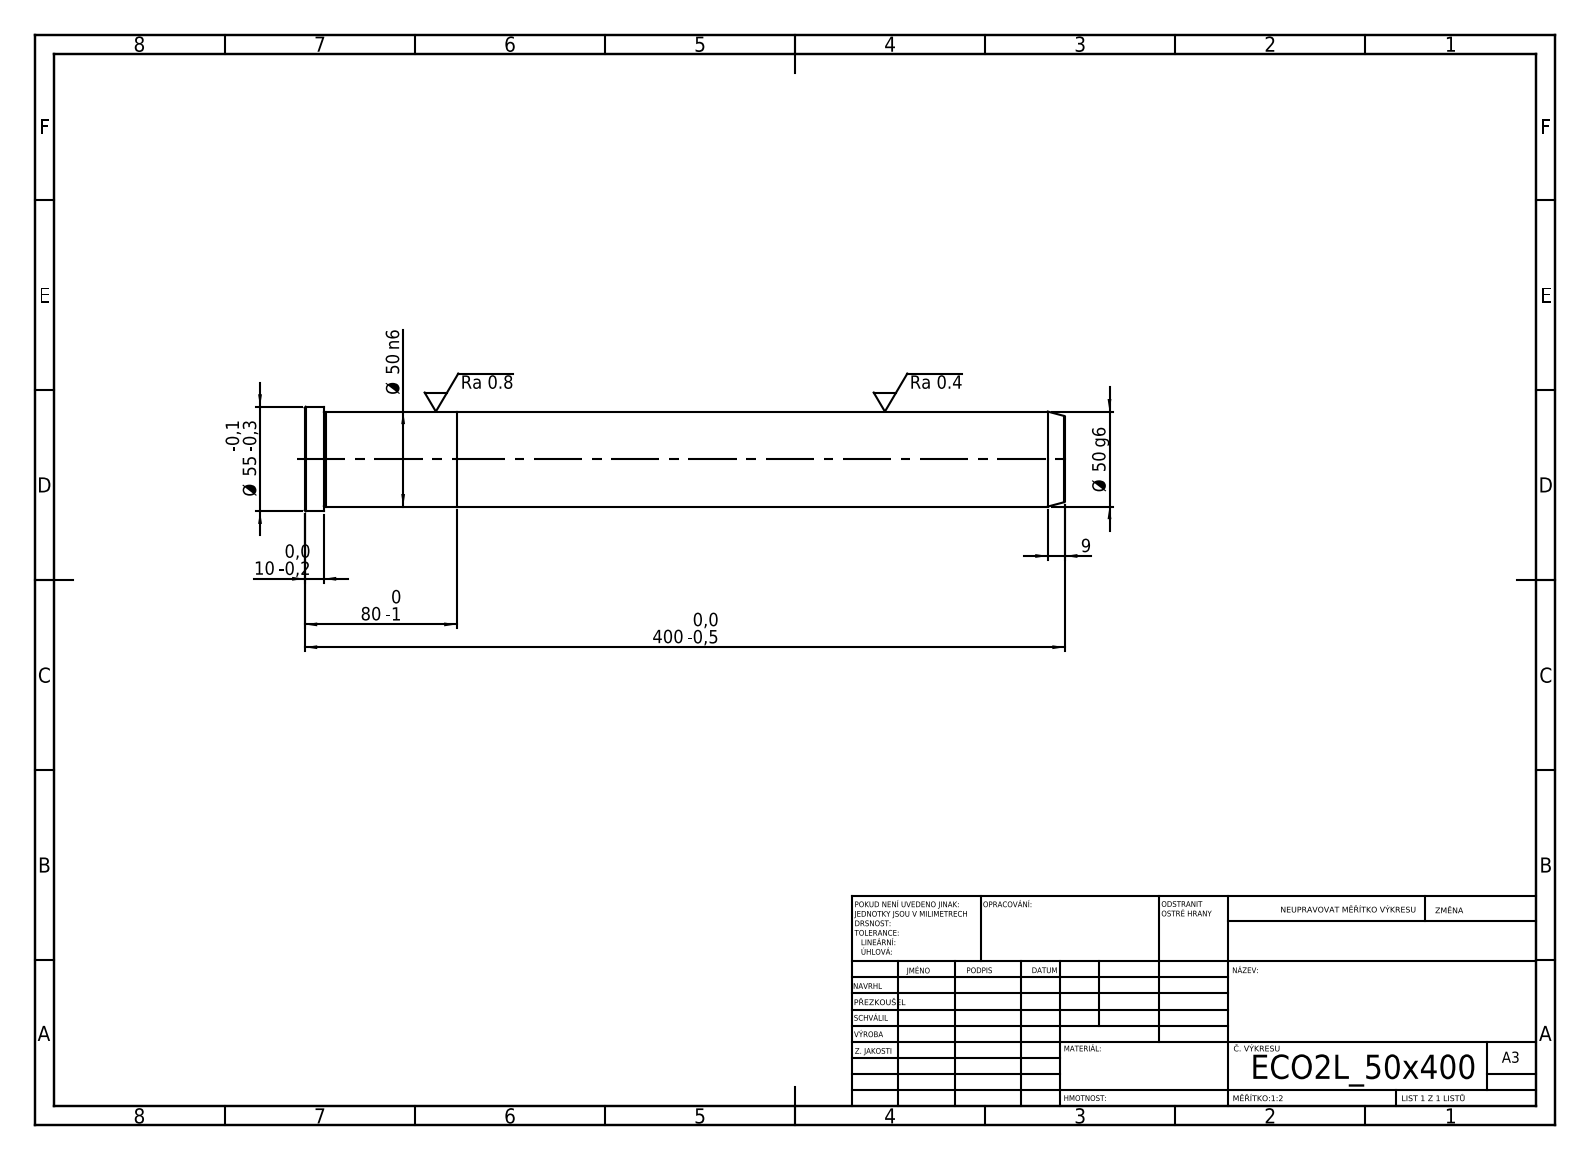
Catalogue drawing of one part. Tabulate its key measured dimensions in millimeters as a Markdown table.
| quantity | value |
| --- | --- |
| STEP written by | SolidWorks 2019 (CONFIG_CONTROL_DESIGN) |
| units | millimeters |
| bodies | 2 solids, 21 faces (5 planar, 6 cylindrical, 10 other) |
| overall size | 400 × 55 × 55 |
| volume | 787 785 mm³ |
| surface area | 71 306 mm² |
| round bosses / shafts (diameter × count) | 55 × 1, 50 × 1 |
| main face-to-face distances | 80, 320, 400, 390, 70, 10 |
